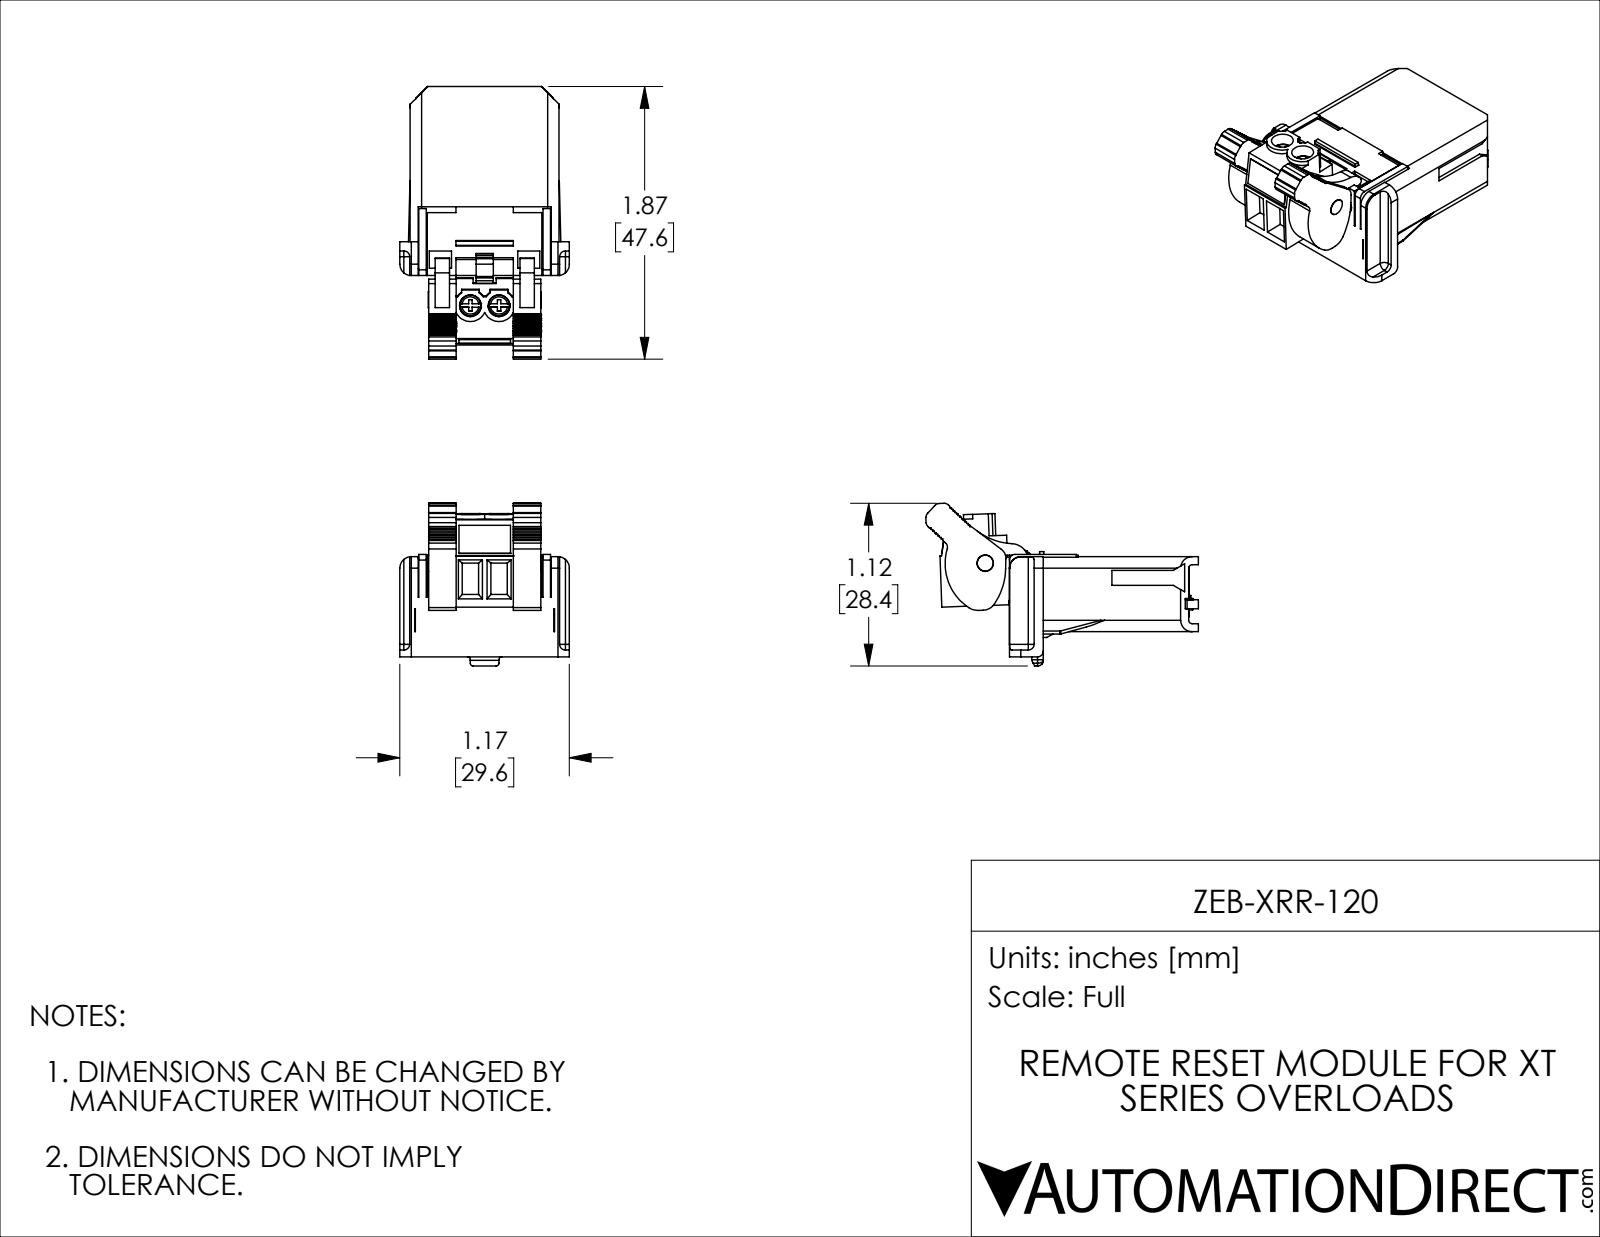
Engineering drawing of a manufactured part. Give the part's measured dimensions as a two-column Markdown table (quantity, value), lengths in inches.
| quantity | value |
| --- | --- |
| part name | ZEB-XRR-120 |
| STEP written by | SolidWorks 2018 (AUTOMOTIVE_DESIGN) |
| units | inches |
| bodies | 1 solid, 1352 faces (1083 planar, 227 cylindrical, 42 other) |
| overall size | 1.874 × 1.165 × 1.119 |
| volume | 0.85 in³ |
| surface area | 10.88 in² |
| round holes (diameter × count) | 0.118 × 2, 0.15 × 2 |
| round bosses / shafts (diameter × count) | 0.143 × 2 |
| partial cylindrical surfaces (radius × count) | 0.005 × 24, 0.039 × 19, 0.008 × 15, 0.01 × 12, 0.02 × 12, 0.079 × 10, 0.024 × 9, 0.004 × 2 |
| main face-to-face distances | 0.516, 0.063, 0.055, 0.031, 0.283, 0.22, 0.028, 1.024, 0.969, 0.173 |
| hole center spacings | 0.196, 0.591 |
